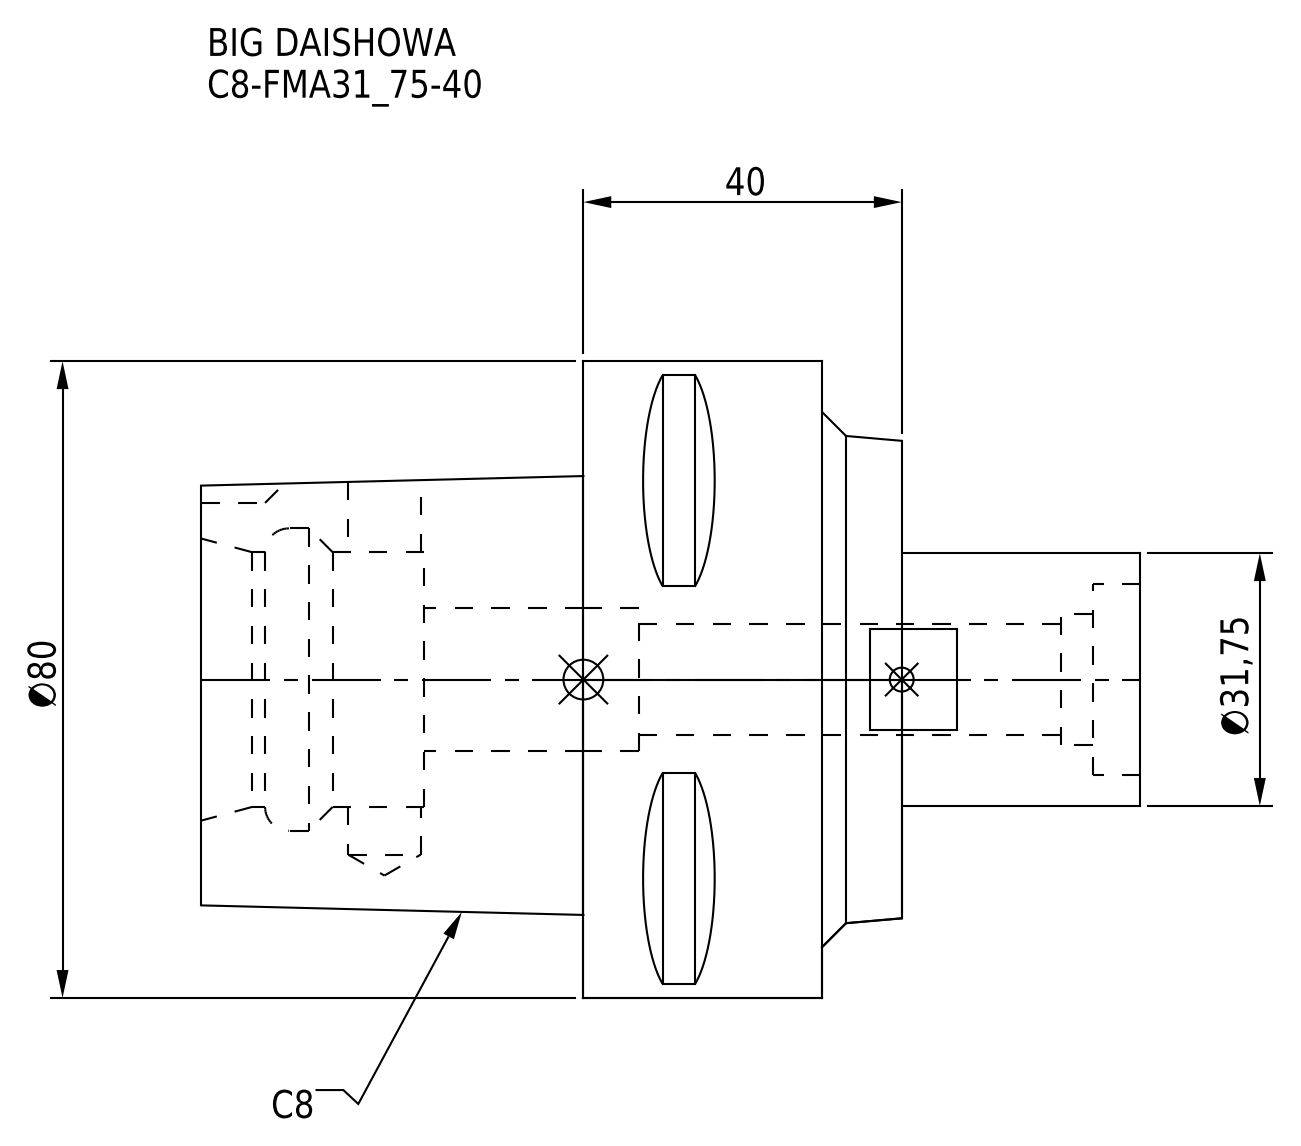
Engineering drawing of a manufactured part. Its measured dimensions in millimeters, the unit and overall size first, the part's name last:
Units: millimetres
Overall size (bounding box): 118 × 80 × 80
Round holes (diameter × count): ⌀9.1 ×1, ⌀14 ×1, ⌀16.5 ×1, ⌀18 ×1, ⌀24 ×1, ⌀32 ×1, ⌀38 ×1
Round bosses / shafts (diameter × count): ⌀80 ×1, ⌀31.75 ×1
Partial cylindrical surfaces — rounded edges, fillets, slot ends (radius × count): R6 ×1
Main face-to-face distances: 40, 30, 10, 88, 78, 48, 20, 60, 50, 28
Volume: 267 176 mm³ · Surface area: 38 867 mm²
Bodies: 1 solid, 84 faces (47 planar, 23 cylindrical, 14 other)
Part name (STEP PRODUCT): C8-FMA31_75-40
STEP written by: CREO PARAMETRIC BY PTC INC, 2016380 (AUTOMOTIVE_DESIGN)
